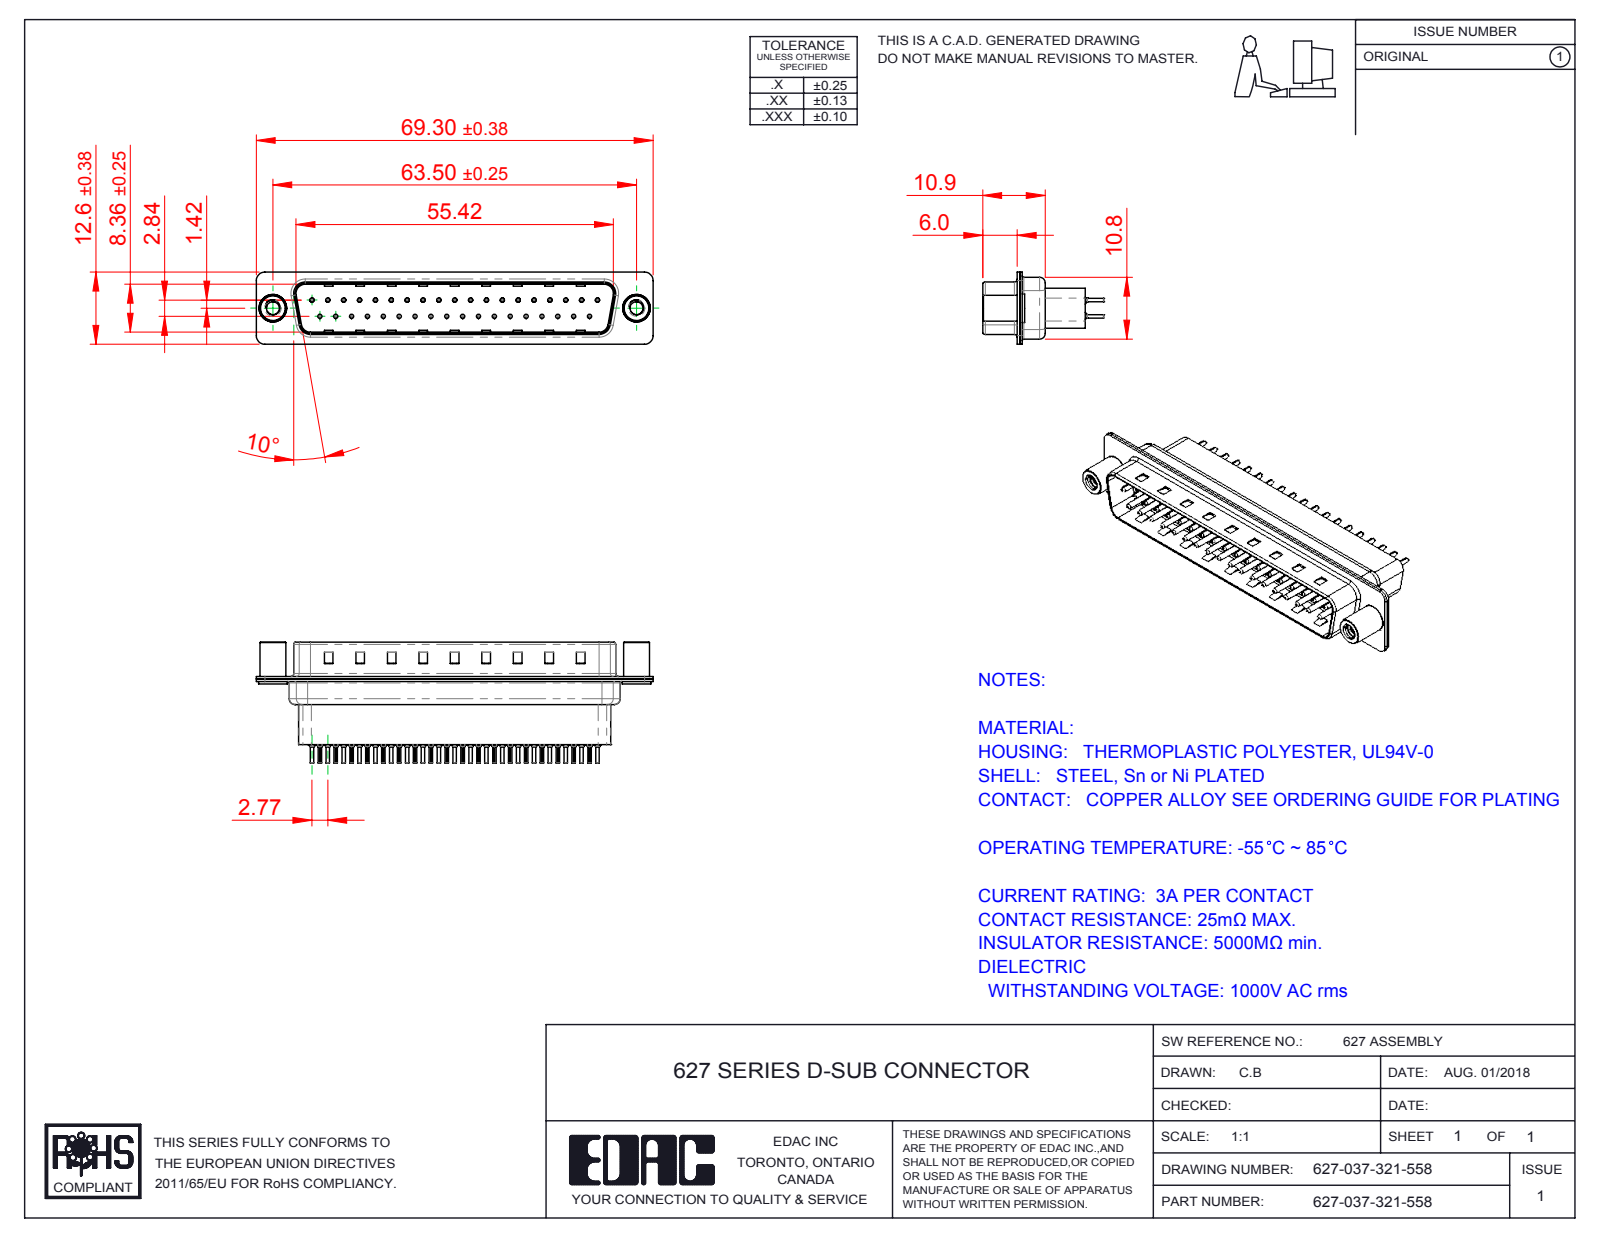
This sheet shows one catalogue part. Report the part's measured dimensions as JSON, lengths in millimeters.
{"part_name": "627 Shell Front_37 Contacts; 627 Shell Rear_37 Contacts; 627 Housing_37 HP; 627 Contact Row 2_21H (+3 more)", "step_written_by": "SolidWorks 2016 (CONFIG_CONTROL_DESIGN)", "units": "millimeters", "bodies": {"solids": 42, "faces": 4072, "planar": 1093, "cylindrical": 1538, "other": 1441}, "overall_size": [69.3, 21.1, 12.6], "volume_mm3": 5534, "surface_area_mm2": 14047, "round_holes": [[0.2, 37], [0.35, 37], [1.1, 37], [1.6, 37], [2.26, 2], [4, 2], [4.8, 2]], "round_bosses_or_shafts": [[2, 37], [1.5, 37], [0.75, 37], [0.6, 37], [5, 2], [4.9, 2], [4.5, 2]], "partial_cylinders_radius": [[0.1, 74], [1.5, 16], [2, 12], [0.5, 8], [1.6, 8], [0.25, 4], [0.6, 4], [0.65, 4]], "face_to_face_distances": [0.4, 0.82, 9.58, 0.68, 7.68, 0.45, 1.5, 1.08, 8.08, 8.76], "hole_center_spacings": [3.16, 2.77, 5.54, 8.31, 5.04, 10.1, 11.08, 12.78]}
